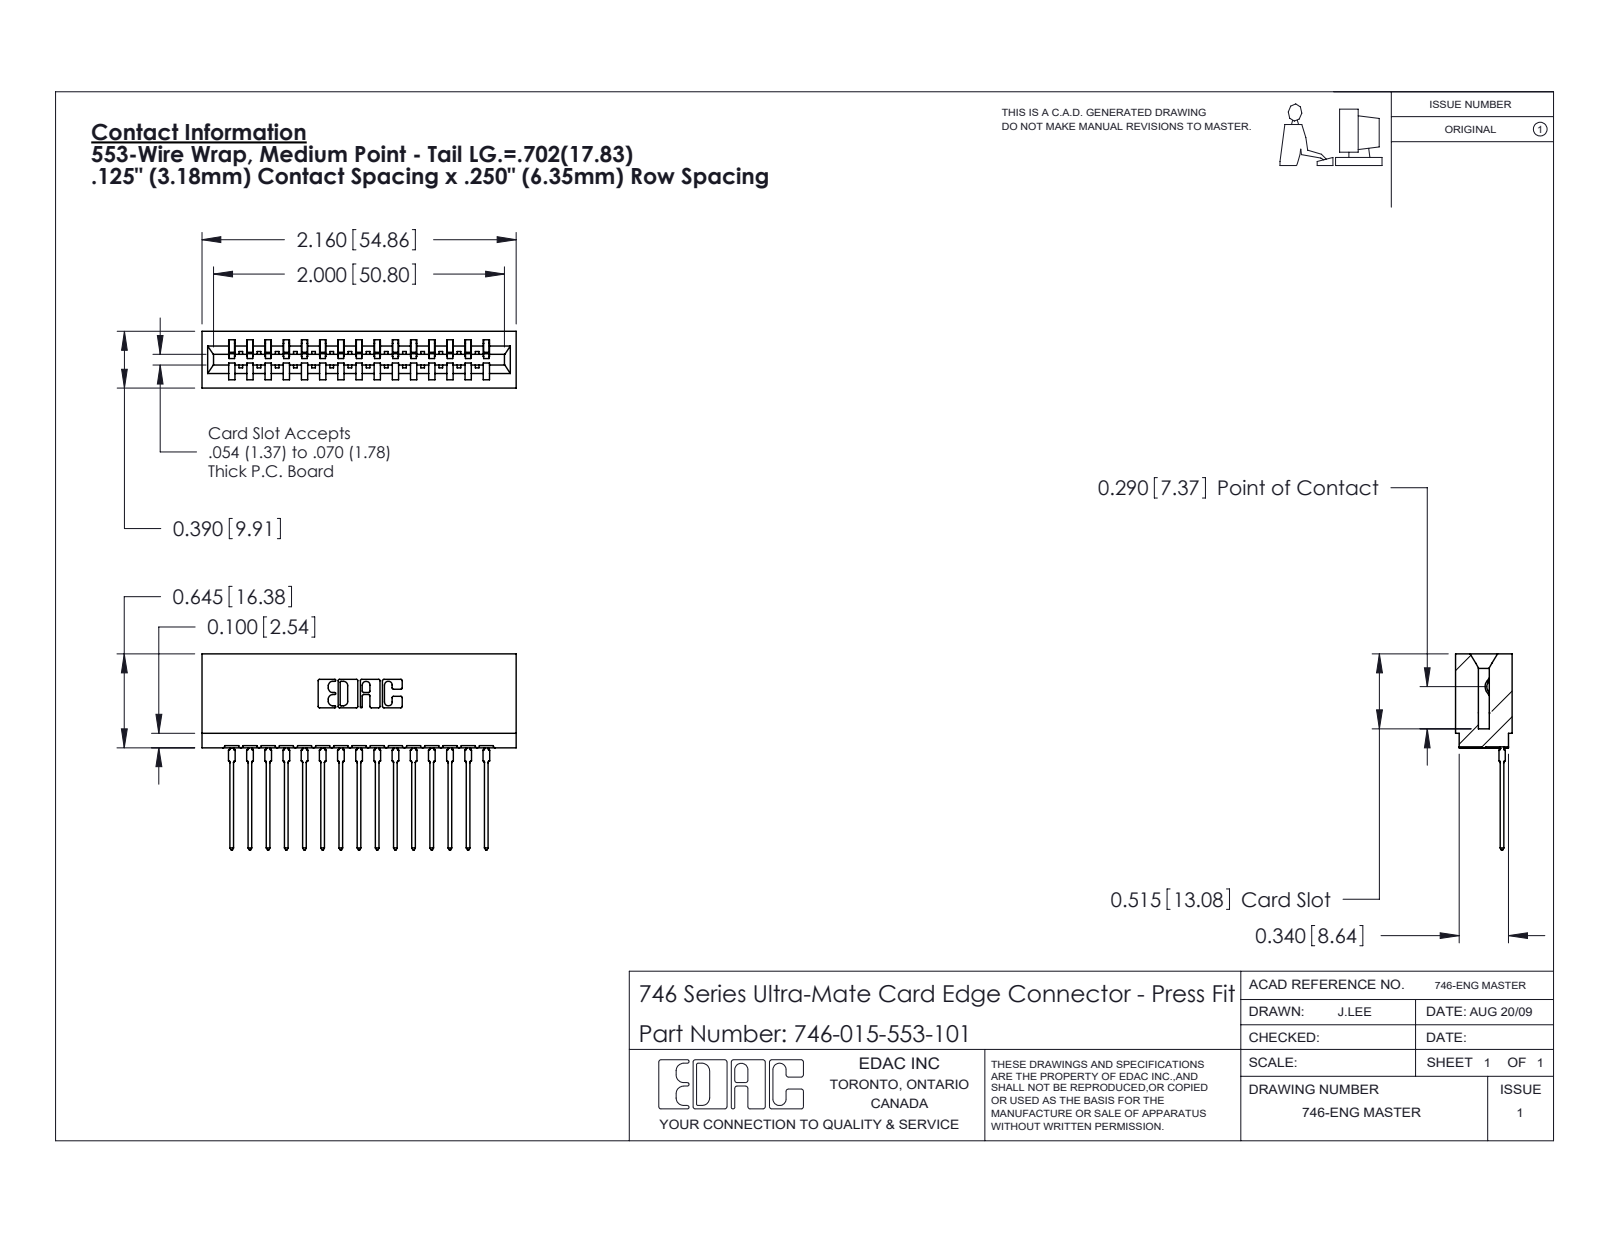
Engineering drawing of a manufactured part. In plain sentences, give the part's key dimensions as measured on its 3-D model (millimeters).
The part is named "746-292-001_553; 746 Part_.515 Slot Depth - 01; 746-015-553-101". Its 3-D file was written by "SolidWorks 2020 (CONFIG_CONTROL_DESIGN)". It is 16 solids with 1717 faces: 1000 planar, 327 cylindrical and 390 other. Overall it measures 54.9 by 34.2 by 9.9 millimeters. Its volume is 5 980 cubic millimeters and its surface area 8 677 square millimeters. Partial cylindrical surfaces (rounded edges, fillets, slot ends): 30 of radius 0.5, 22 of radius 0.3, 16 of radius 0.4, 6 of radius 0.2, 6 of radius 0.8, 4 of radius 0.1, 4 of radius 0.3, 3 of radius 0.7. The main face-to-face distances are 6.4, 8.5, 1.4, 12.7, 9.9, 1.1, 3.2, 0.6, 9.5, 5.3.
